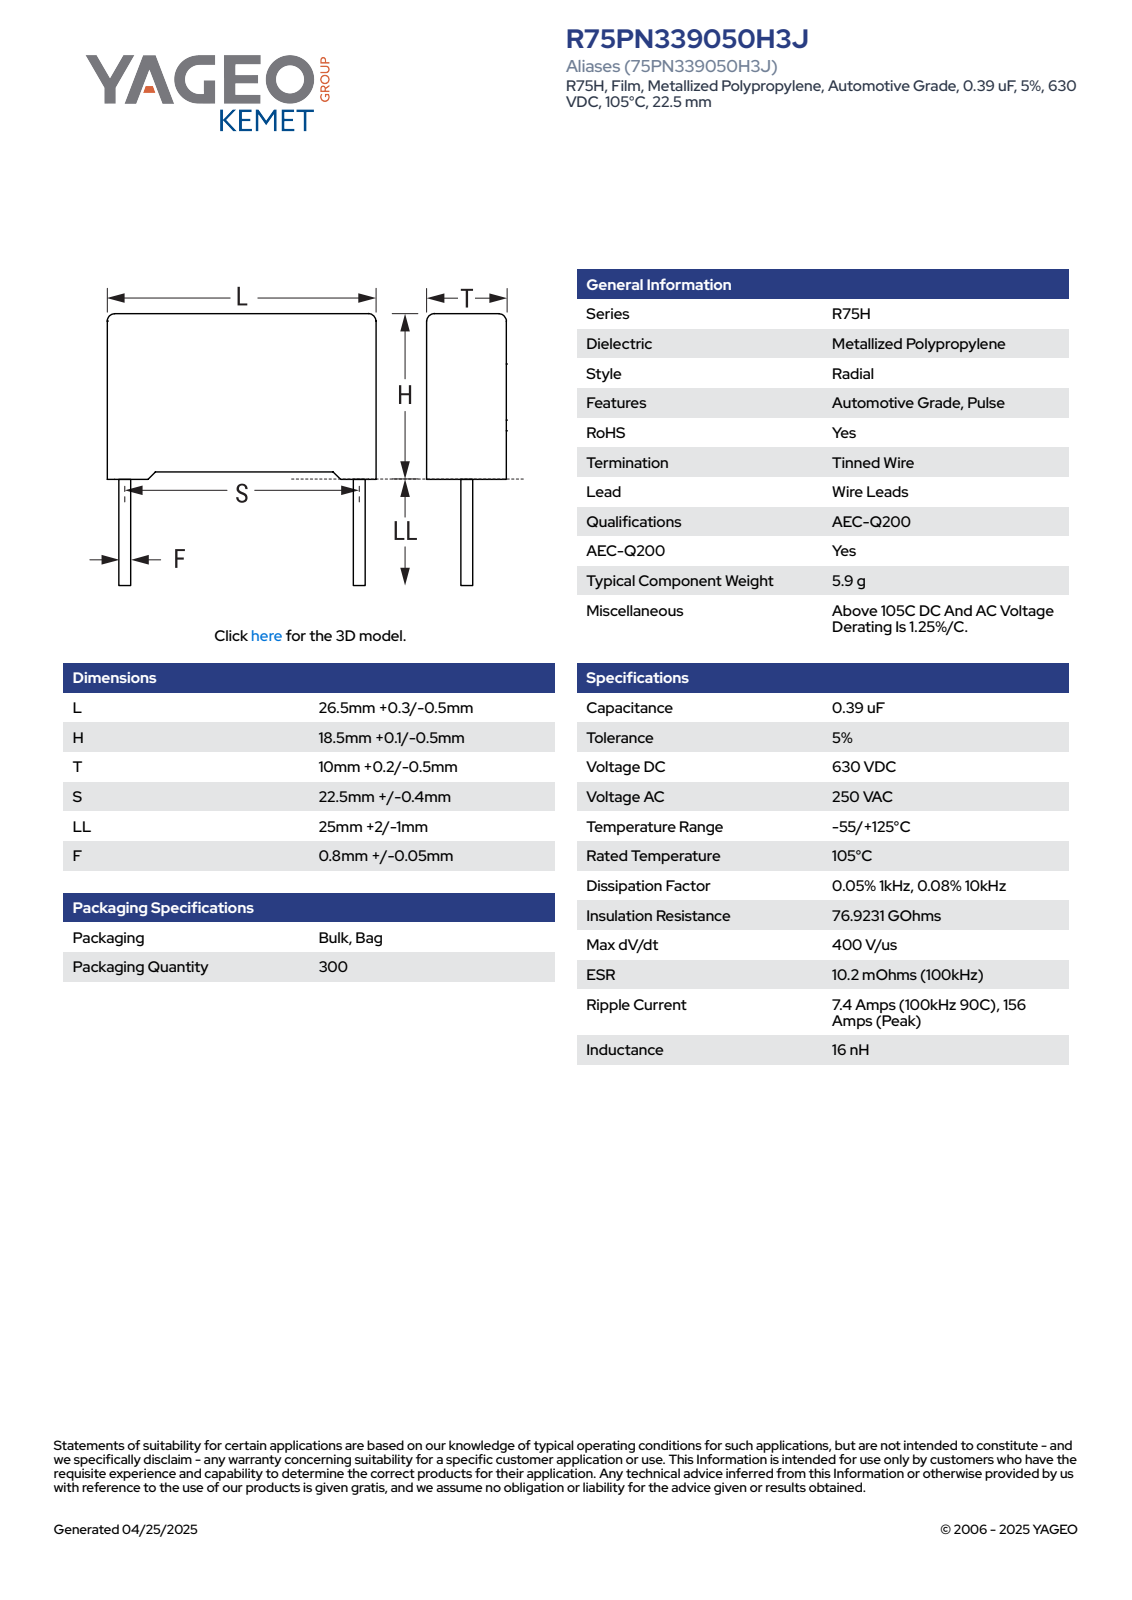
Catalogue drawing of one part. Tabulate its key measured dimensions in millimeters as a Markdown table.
| quantity | value |
| --- | --- |
| part name | CFR_RB2_26.5X18.5X10_L26.8H18.6T10.2S22.5LL27F0.85 |
| STEP written by | SolidWorks 2021 (AUTOMOTIVE_DESIGN) |
| units | millimeters |
| bodies | 4 solids, 85 faces (77 planar, 8 cylindrical, 0 other) |
| overall size | 45.6 × 26.8 × 10.21 |
| volume | 4 933 mm³ |
| surface area | 2 112 mm² |
| round bosses / shafts (diameter × count) | 0.85 × 2 |
| partial cylindrical surfaces (radius × count) | 0.5 × 4 |
| main face-to-face distances | 10.2, 17.85, 26.8, 17.96, 0.75, 0.64, 18.6, 0.89, 9.31, 25.91 |
